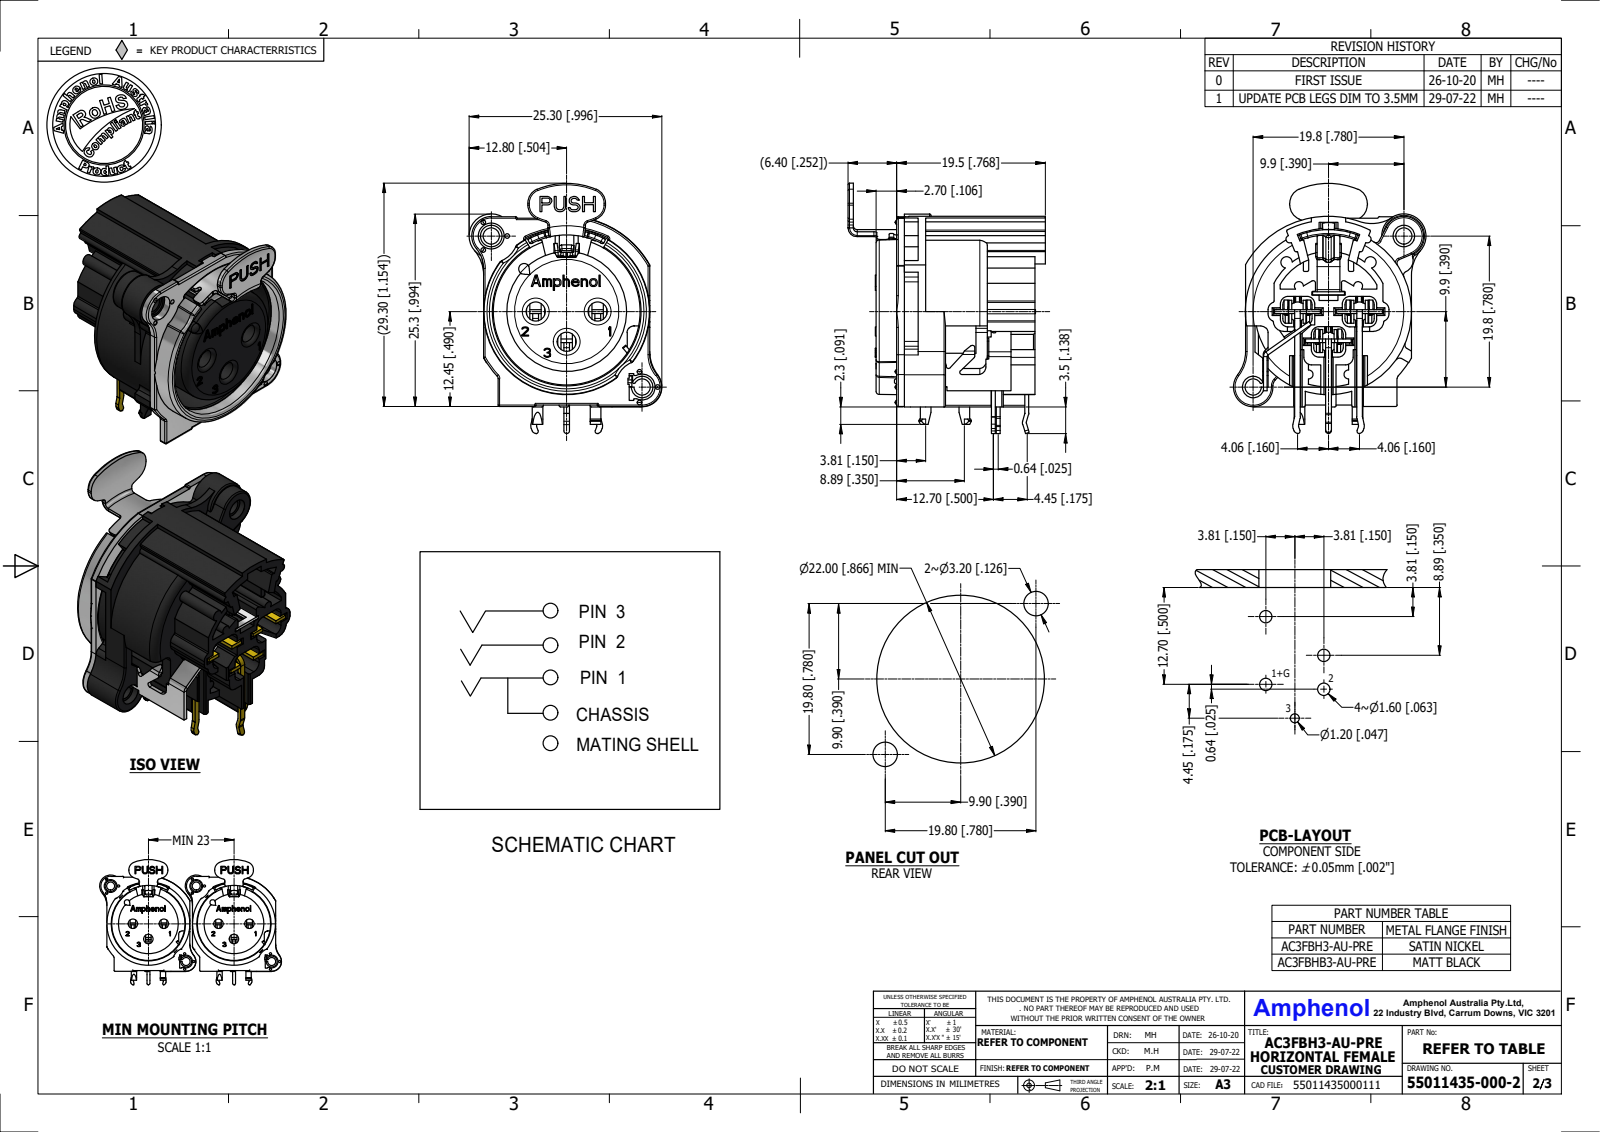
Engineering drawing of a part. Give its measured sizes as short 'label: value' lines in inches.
name: AC3FBH3-AU-PRE simplified
written by: Autodesk Inventor 2023 (AUTOMOTIVE_DESIGN)
unit: in
bodies: 1 solid, 1219 faces (870 planar, 239 cylindrical, 110 other)
size: 1.293 × 1.02 × 0.996
volume: 0.439 in³; area: 6.831 in²
holes: 3× ⌀0.098, 2× ⌀0.045, 2× ⌀0.083, 2× ⌀0.11, 1× ⌀0.047, 1× ⌀0.134, 1× ⌀0.76, 1× ⌀0.768, 1× ⌀0.813
bosses: 2× ⌀0.055, 2× ⌀0.047, 1× ⌀0.809, 1× ⌀0.618
rounds: 47× R0.008, 23× R0.039, 18× R0.02, 13× R0.012, 12× R0.016, 8× R0.006, 8× R0.024, 4× R0.079
face distances: 0.706, 0.039, 0.469, 0.146, 0.115, 0.821, 0.715, 0.106, 0.429, 0.575
hole spacings: 0.16, 0.223, 0.452, 0.551, 0.674, 0.115, 0.135, 0.156
